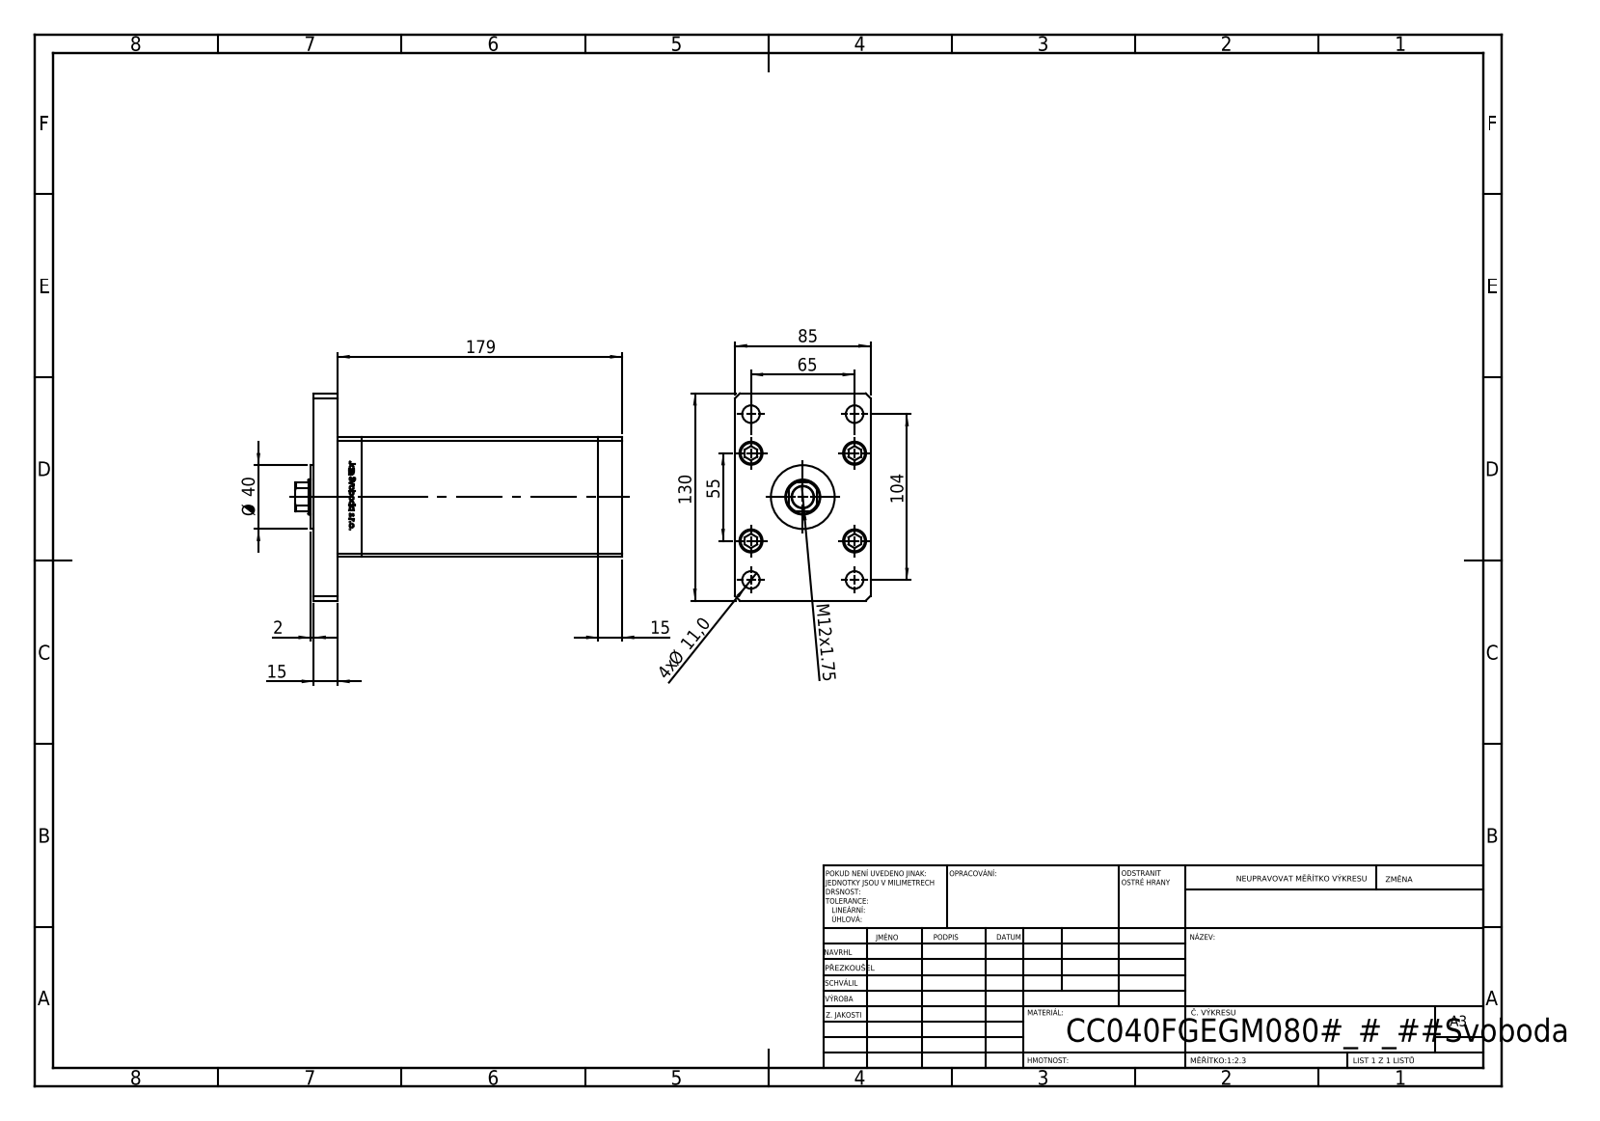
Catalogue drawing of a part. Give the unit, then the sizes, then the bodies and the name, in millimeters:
Units: millimetres
Overall size (bounding box): 205 × 130 × 85
Round holes (diameter × count): ⌀11 ×9, ⌀15.5 ×5, ⌀10 ×4, ⌀14.5 ×4, ⌀2 ×2, ⌀13.16 ×2, ⌀13.5 ×1, ⌀22 ×1, ⌀23.5 ×1
Round bosses / shafts (diameter × count): ⌀8 ×9, ⌀14.5 ×5, ⌀40 ×1
Partial cylindrical surfaces — rounded edges, fillets, slot ends (radius × count): R0.93 ×2, R10.5 ×1
Main face-to-face distances: 15, 85, 163.5, 178.5, 75, 30, 148.5, 193.5, 10.5, 27.5
Hole centre spacings: 28, 24.5, 42.57, 61.32, 65, 69.46, 79.5, 102.69
Volume: 1 165 000 mm³ · Surface area: 198 888 mm²
Bodies: 19 solids, 1310 faces (517 planar, 187 cylindrical, 606 other)
Part name (STEP PRODUCT): V220C BACK_F; ALLEN BOLT; V220C_FRONT_F; V220C_F (+2 more)
STEP written by: SolidWorks 2019 (CONFIG_CONTROL_DESIGN)
